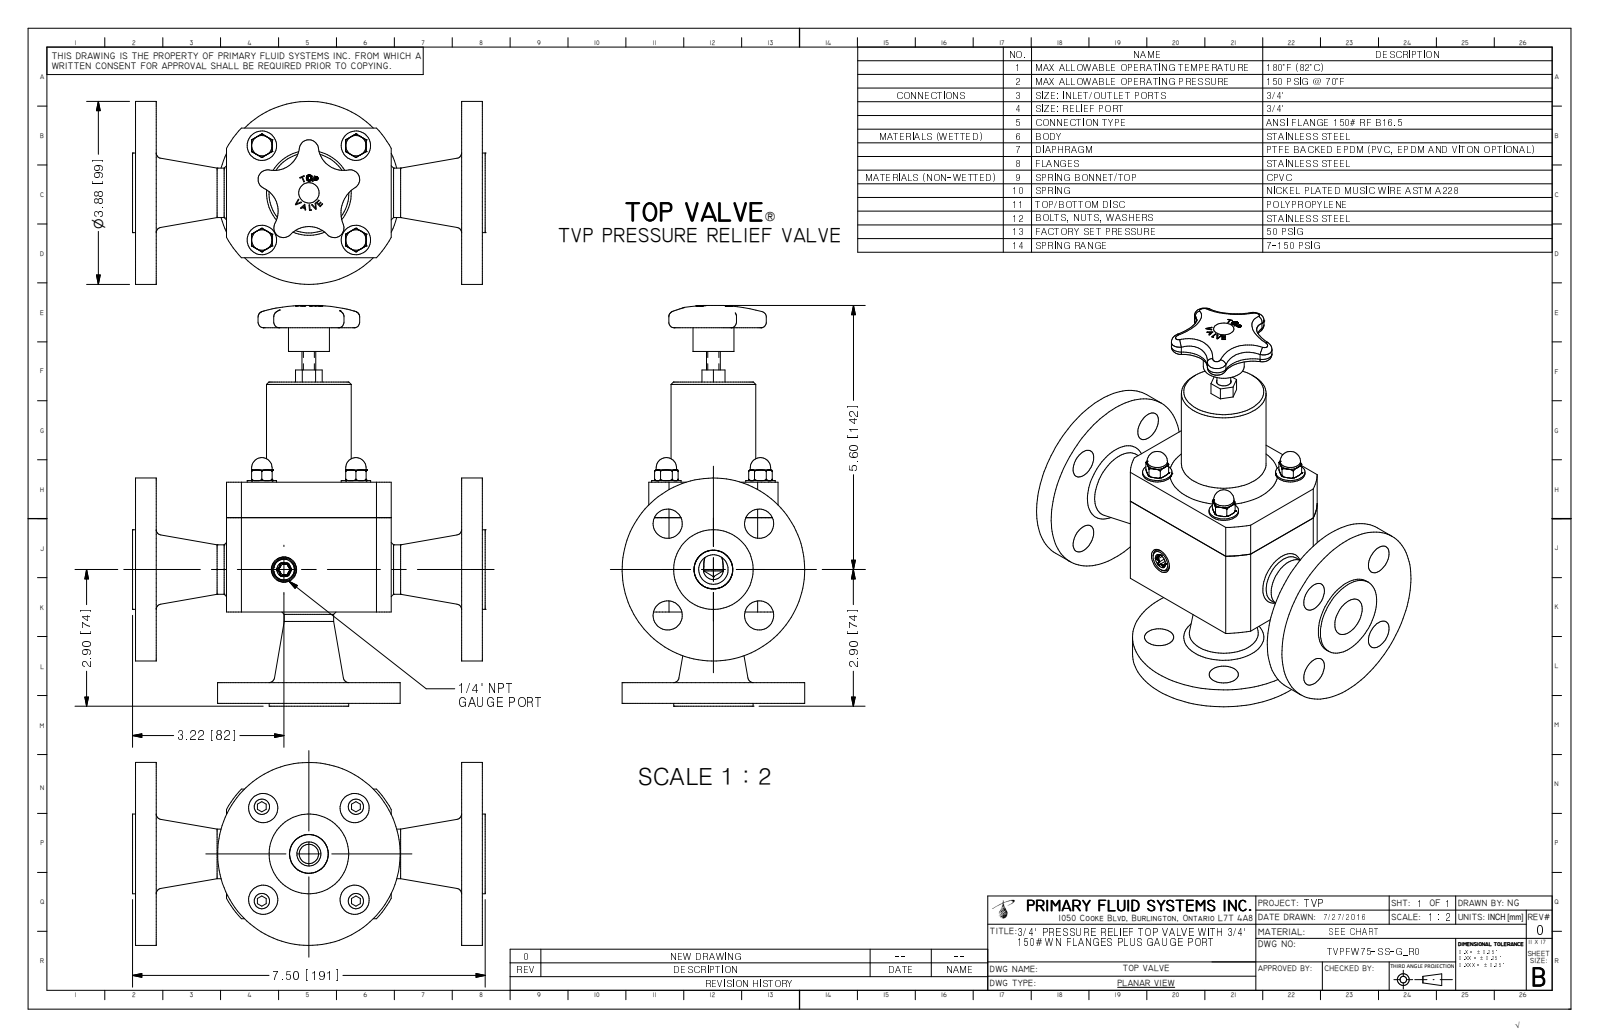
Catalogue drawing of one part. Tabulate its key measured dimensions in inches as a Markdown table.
| quantity | value |
| --- | --- |
| part name | TVPFW75-SS-G_R0 |
| STEP written by | Autodesk Inventor 2009 (AUTOMOTIVE_DESIGN) |
| units | inches |
| bodies | 1 solid, 374 faces (140 planar, 71 cylindrical, 163 other) |
| overall size | 8.499 × 7.5 × 3.88 |
| volume | 49.57 in³ |
| surface area | 193.3 in² |
| round holes (diameter × count) | 0.62 × 8, 0.175 × 4, 0.824 × 2, 2.4 × 1 |
| round bosses / shafts (diameter × count) | 0.625 × 4, 0.433 × 4, 3.88 × 2, 1.69 × 2, 1.05 × 2, 2.375 × 1, 1.8 × 1, 0.87 × 1 |
| partial cylindrical surfaces (radius × count) | 0.027 × 6, 0.085 × 5, 0.205 × 5, 0.536 × 4, 0.656 × 4, 0.625 × 1, 0.745 × 1, 1.988 × 1 |
| main face-to-face distances | 0.44, 6.935, 1.937, 5.437, 1.498, 4.998, 1.937, 7.375, 0.44, 1.497 |
| hole center spacings | 1.375, 1.945, 1.972, 0.039, 1.414, 2, 2.75, 2.789 |
